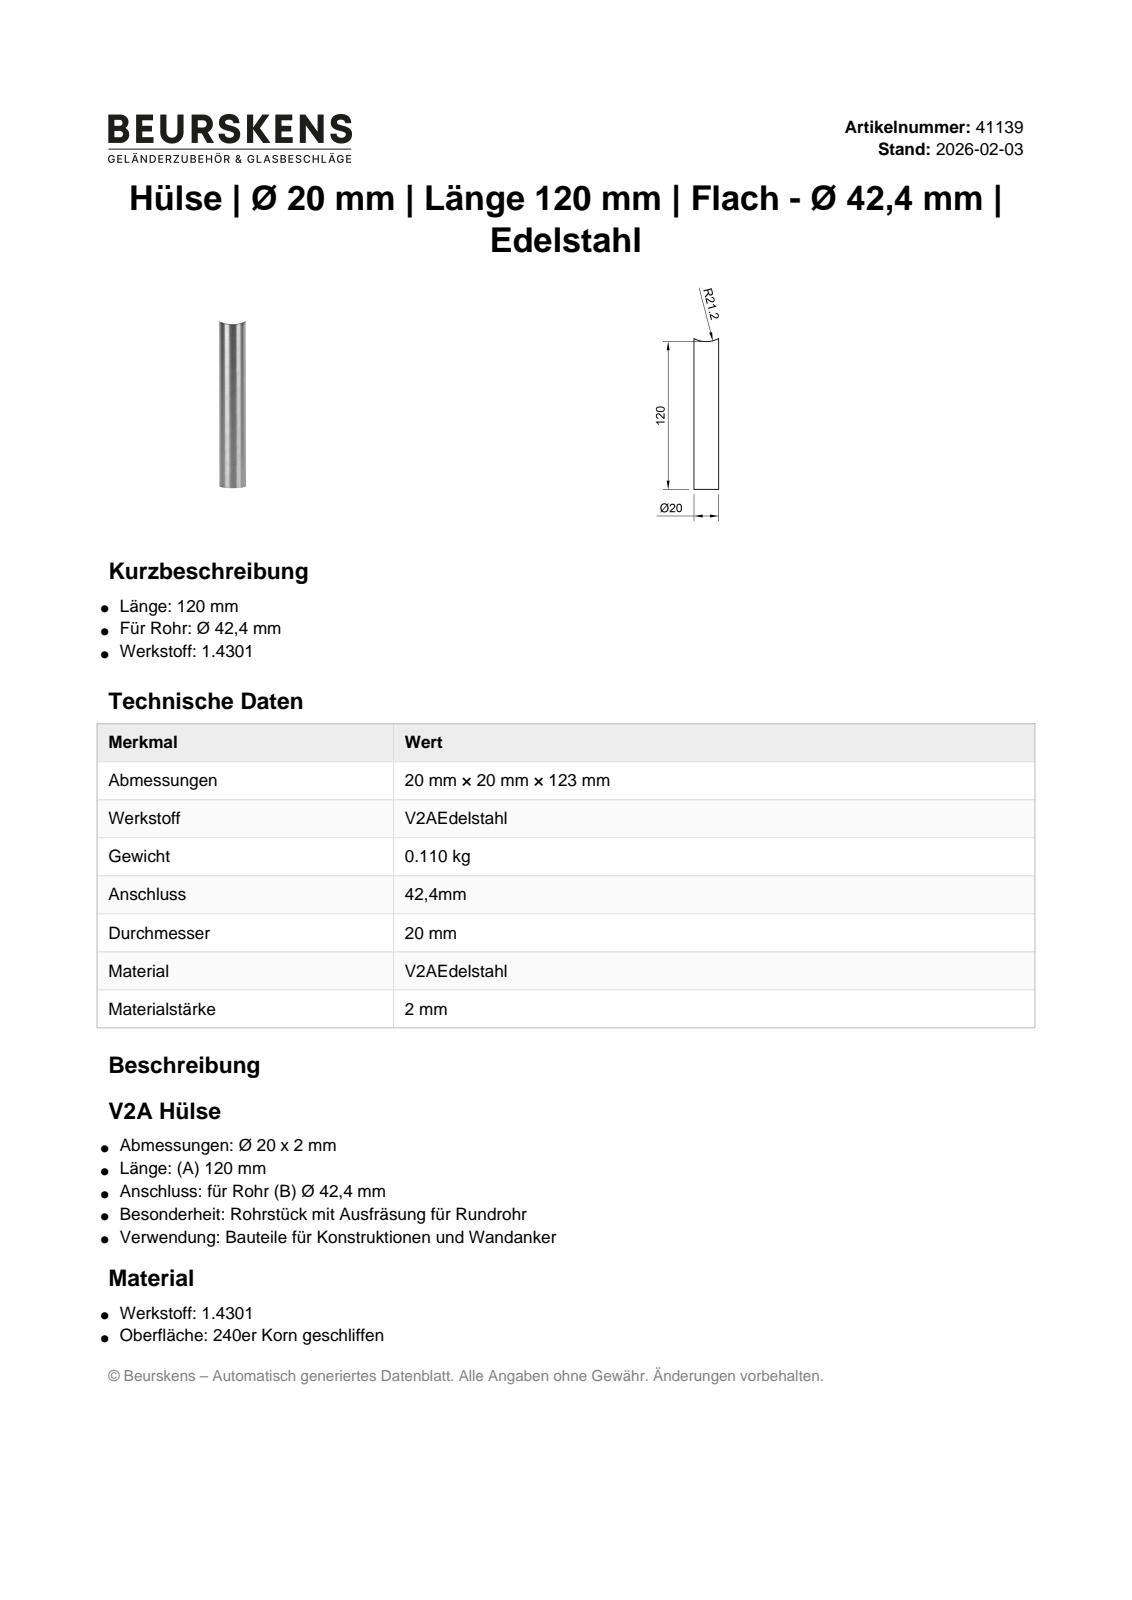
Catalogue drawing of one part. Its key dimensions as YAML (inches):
part_name: "41139"
step_written_by: "Autodesk Inventor 2022 (AUTOMOTIVE_DESIGN)"
units: inches
bodies: {solids: 1, faces: 4, planar: 1, cylindrical: 3, other: 0}
overall_size: [4.823, 0.787, 0.787]
volume: 0.441
surface_area: 22.6
round_holes:
  - {diameter: 0.709, count: 1}
round_bosses_or_shafts:
  - {diameter: 0.787, count: 1}
partial_cylinders:
  - {radius: 0.835, count: 1}
